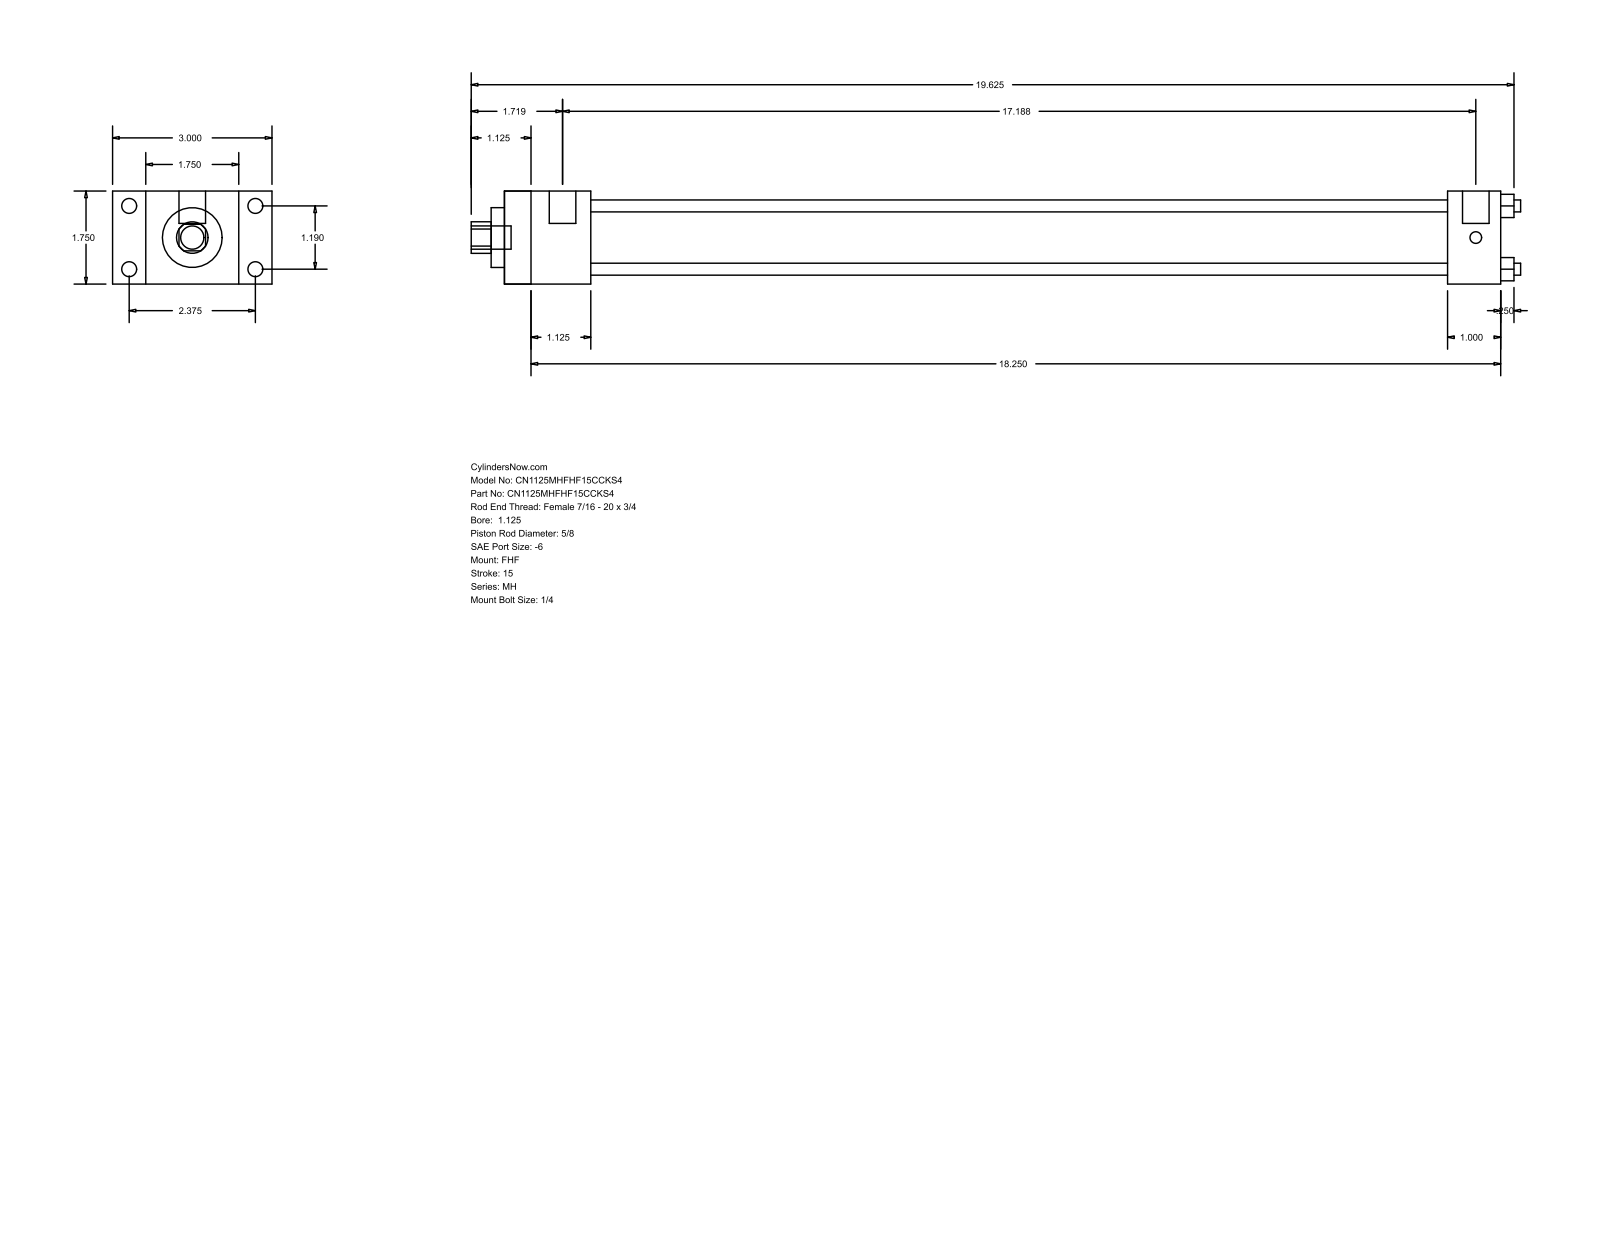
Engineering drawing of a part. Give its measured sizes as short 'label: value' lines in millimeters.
name: MH_FHF__0112_0.625
written by: GSSL Pune (CONFIG_CONTROL_DESIGN)
unit: mm
bodies: 0 solids, 88 faces (60 planar, 28 cylindrical, 0 other)
size: 501.65 × 76.2 × 44.45
holes: 4× ⌀5.71, 1× ⌀15.88, 1× ⌀28.57, 1× ⌀34.92
bosses: 4× ⌀7.14, 4× ⌀5.56, 2× ⌀12.7, 1× ⌀11.11
rounds: 1× R7.54
face distances: 44.46, 15.87, 60.33, 41.27, 76.2, 476.24, 434.97, 450.85, 409.58, 25.39
hole spacings: 21.37, 30.22, 42.74
